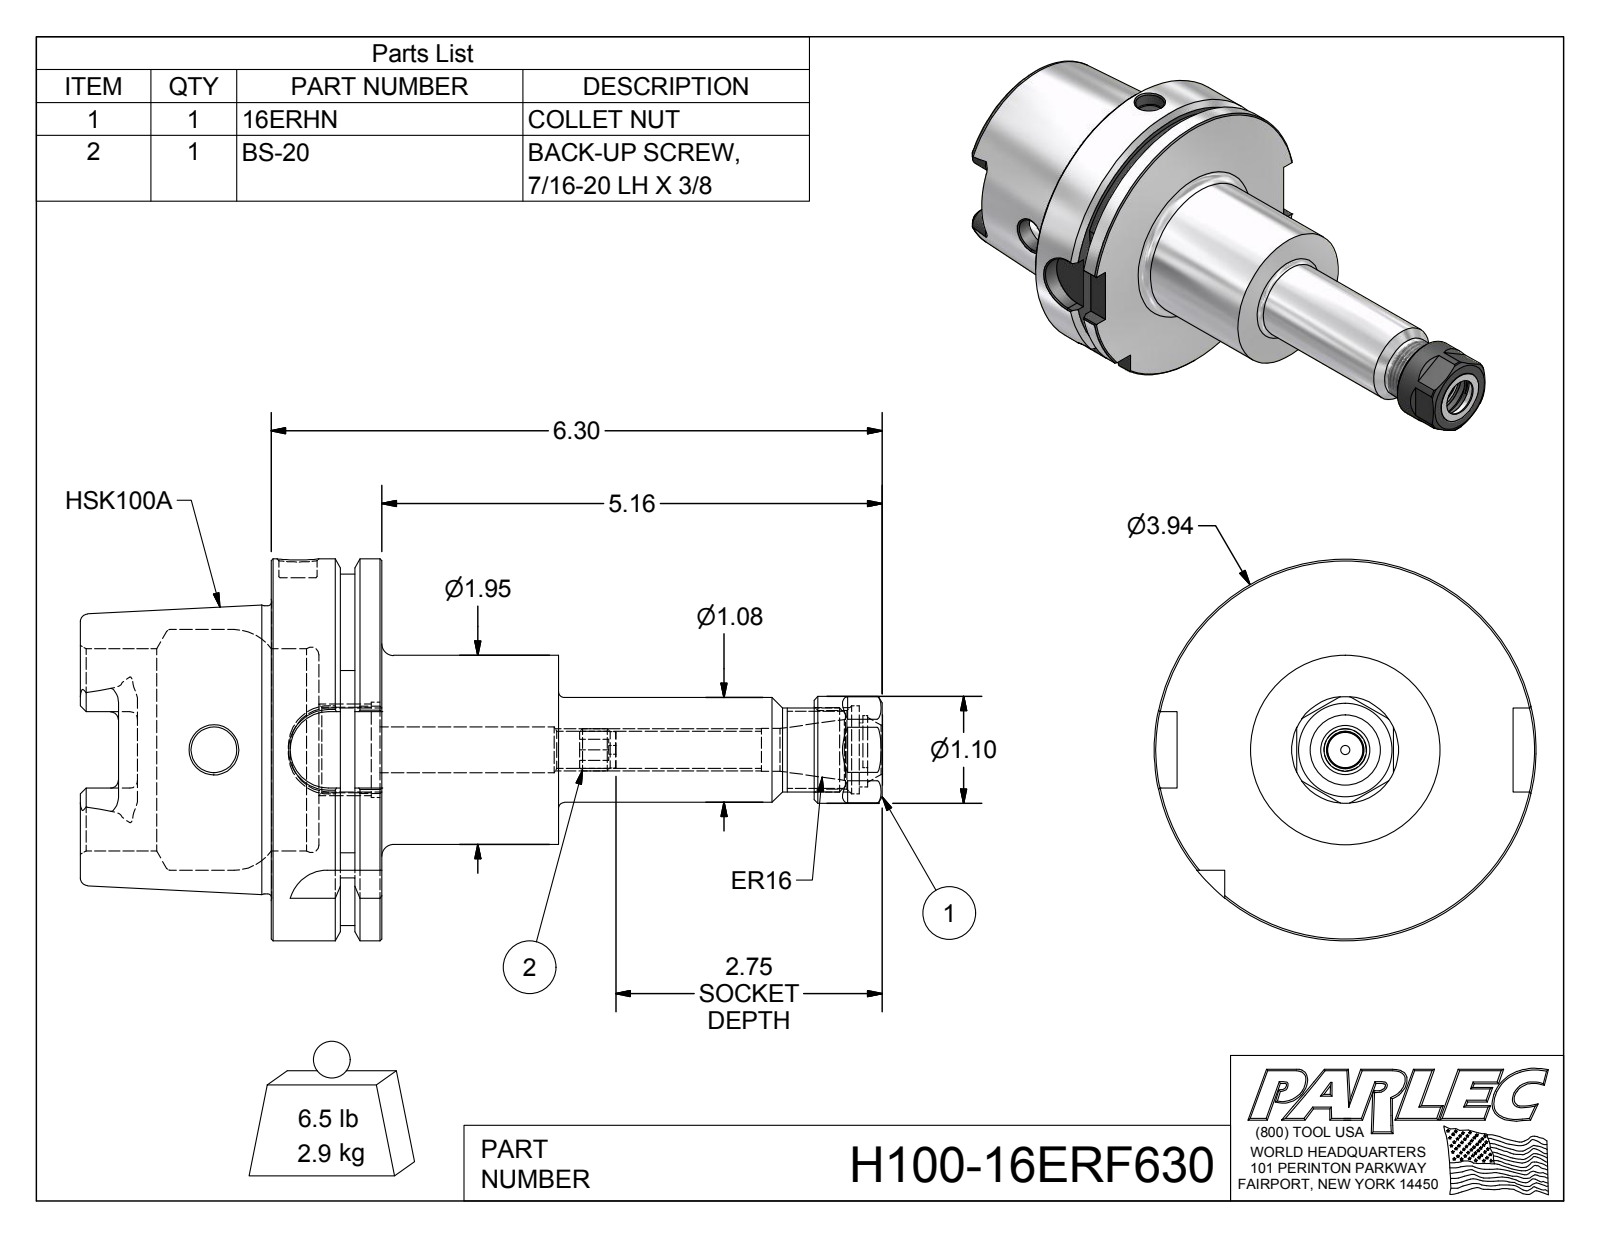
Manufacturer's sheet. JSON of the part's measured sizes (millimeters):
{"part_name": "H100-16ER6-1; 16ERHN; BS-20; H100-16ERF630", "step_written_by": "Autodesk Inventor 2016 (AUTOMOTIVE_DESIGN)", "units": "millimeters", "bodies": {"solids": 3, "faces": 187, "planar": 69, "cylindrical": 49, "other": 69}, "overall_size": [210.02, 100, 100], "volume_mm3": 377132, "surface_area_mm2": 71190, "round_holes": [[9, 2], [12, 2], [2.29, 1], [9.73, 1], [10, 1], [11.18, 1], [11.99, 1], [12.4, 1], [17.02, 1], [20.5, 1], [22.38, 1], [23, 1]], "round_bosses_or_shafts": [[100, 1], [92, 1], [75.36, 1], [49.53, 1], [28, 1], [27.43, 1], [22, 1], [10.97, 1]], "partial_cylinders_radius": [[2, 6], [4.88, 4], [10, 4], [7.24, 1], [9, 1]], "face_to_face_distances": [29, 12.5, 16.5, 75.23, 62.73, 46.23, 50, 62.5, 79, 125.23], "hole_center_spacings": [1.52]}
